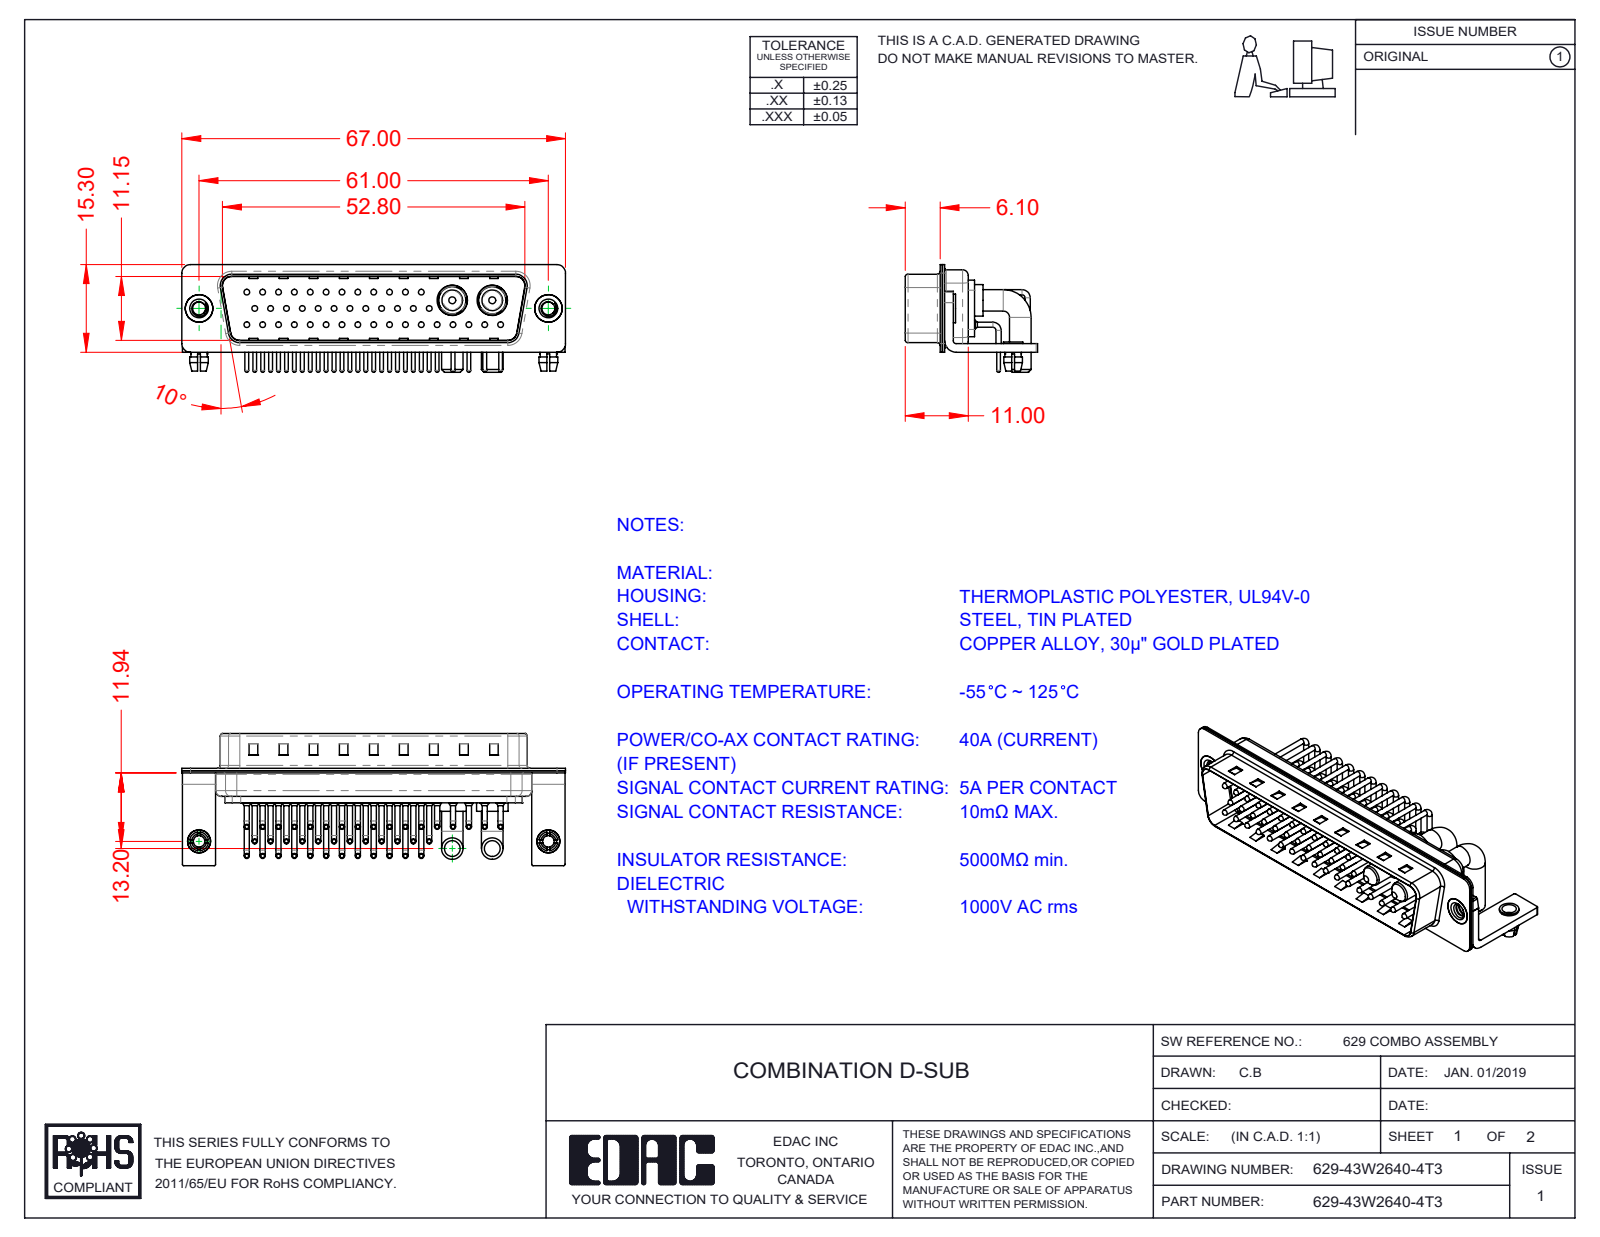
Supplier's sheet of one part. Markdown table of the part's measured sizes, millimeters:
| quantity | value |
| --- | --- |
| part name | 629Combo Stabilizer Bracket_50 Contacts; 629Combo Board Lock_50 Contacts; 629-43W2640-4T3; 629Combo Contact Row 3 (+7 more) |
| STEP written by | SolidWorks 2020 (CONFIG_CONTROL_DESIGN) |
| units | millimeters |
| bodies | 54 solids, 5140 faces (2915 planar, 1709 cylindrical, 516 other) |
| overall size | 67 × 23.1 × 18.8 |
| volume | 5 757 mm³ |
| surface area | 13 603 mm² |
| round holes (diameter × count) | 2 × 43, 0.75 × 41, 1.6 × 41, 2.26 × 2, 2.5 × 2, 3.2 × 2, 4 × 2, 4.8 × 2, 4.85 × 2, 5.3 × 2 |
| round bosses / shafts (diameter × count) | 0.9 × 82, 1.5 × 41, 1 × 41, 0.65 × 41, 3.75 × 4, 5.5 × 2, 5.2 × 2, 5 × 2 |
| partial cylindrical surfaces (radius × count) | 1.01 × 41, 0.25 × 16, 1.5 × 16, 2 × 13, 0.5 × 9, 1.6 × 8, 0.6 × 4, 0.65 × 4 |
| main face-to-face distances | 0.4, 1.5, 11.55, 5.6, 5.2, 0.8, 1.9, 4.1, 6, 0.78 |
| hole center spacings | 2.77, 5.54, 3.16, 8.31, 11.08, 13.85, 16.62, 19.39 |
